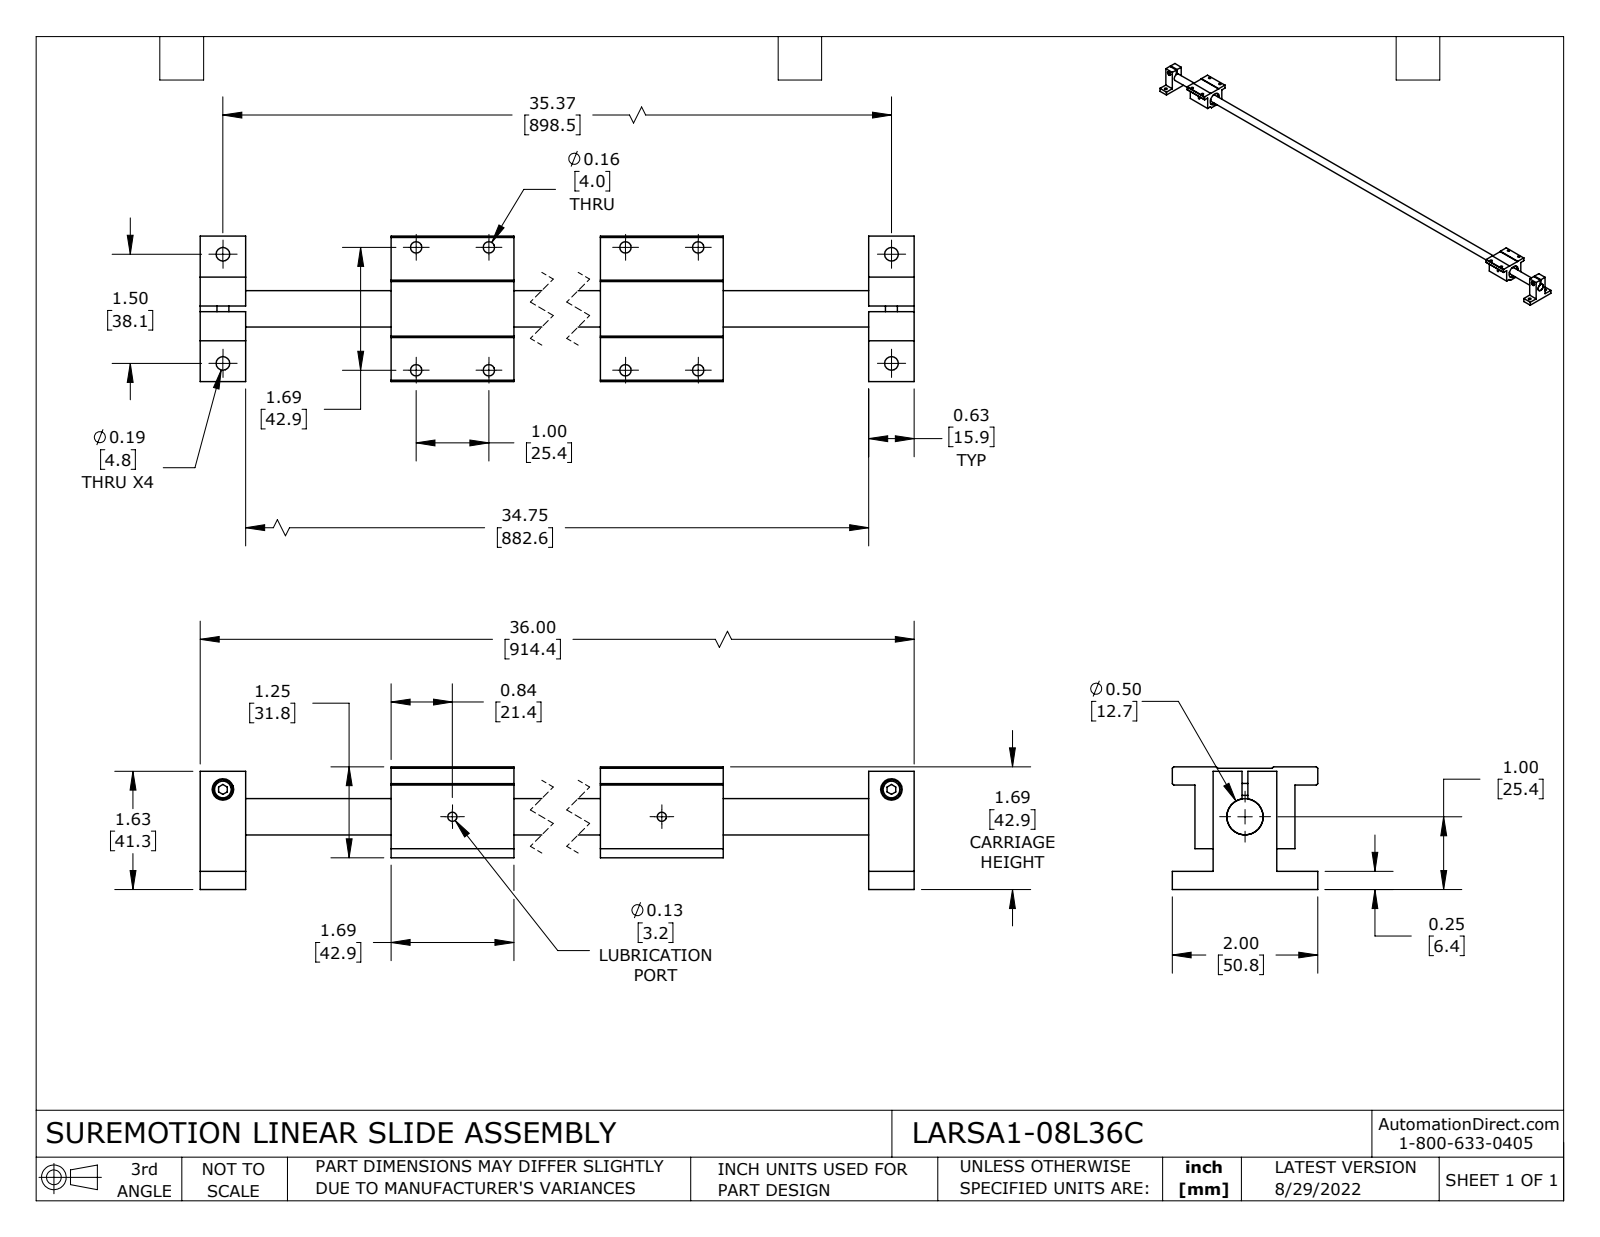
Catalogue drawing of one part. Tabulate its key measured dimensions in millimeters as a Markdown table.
| quantity | value |
| --- | --- |
| part name | LARSA1-08L36C_RAIL; LARSACC-001; LARSA1-08L36C |
| STEP written by | SolidWorks 2021 (CONFIG_CONTROL_DESIGN) |
| units | millimeters |
| bodies | 7 solids, 160 faces (96 planar, 60 cylindrical, 4 other) |
| overall size | 914.4 × 50.8 × 42.8 |
| volume | 228 400 mm³ |
| surface area | 71 290 mm² |
| round holes (diameter × count) | 4 × 8, 4.8 × 4, 3.2 × 2, 7.5 × 2, 12.7 × 1, 22.2 × 1 |
| round bosses / shafts (diameter × count) | 6.9 × 2, 4.2 × 2 |
| main face-to-face distances | 6.4, 28.6, 34.9, 50.8, 22.2, 738.1, 36.5, 898.5, 15.9, 0.5 |
| hole center spacings | 738.1, 25.4, 42.9, 49.8, 67.5, 78.7, 92.9, 101.3 |
